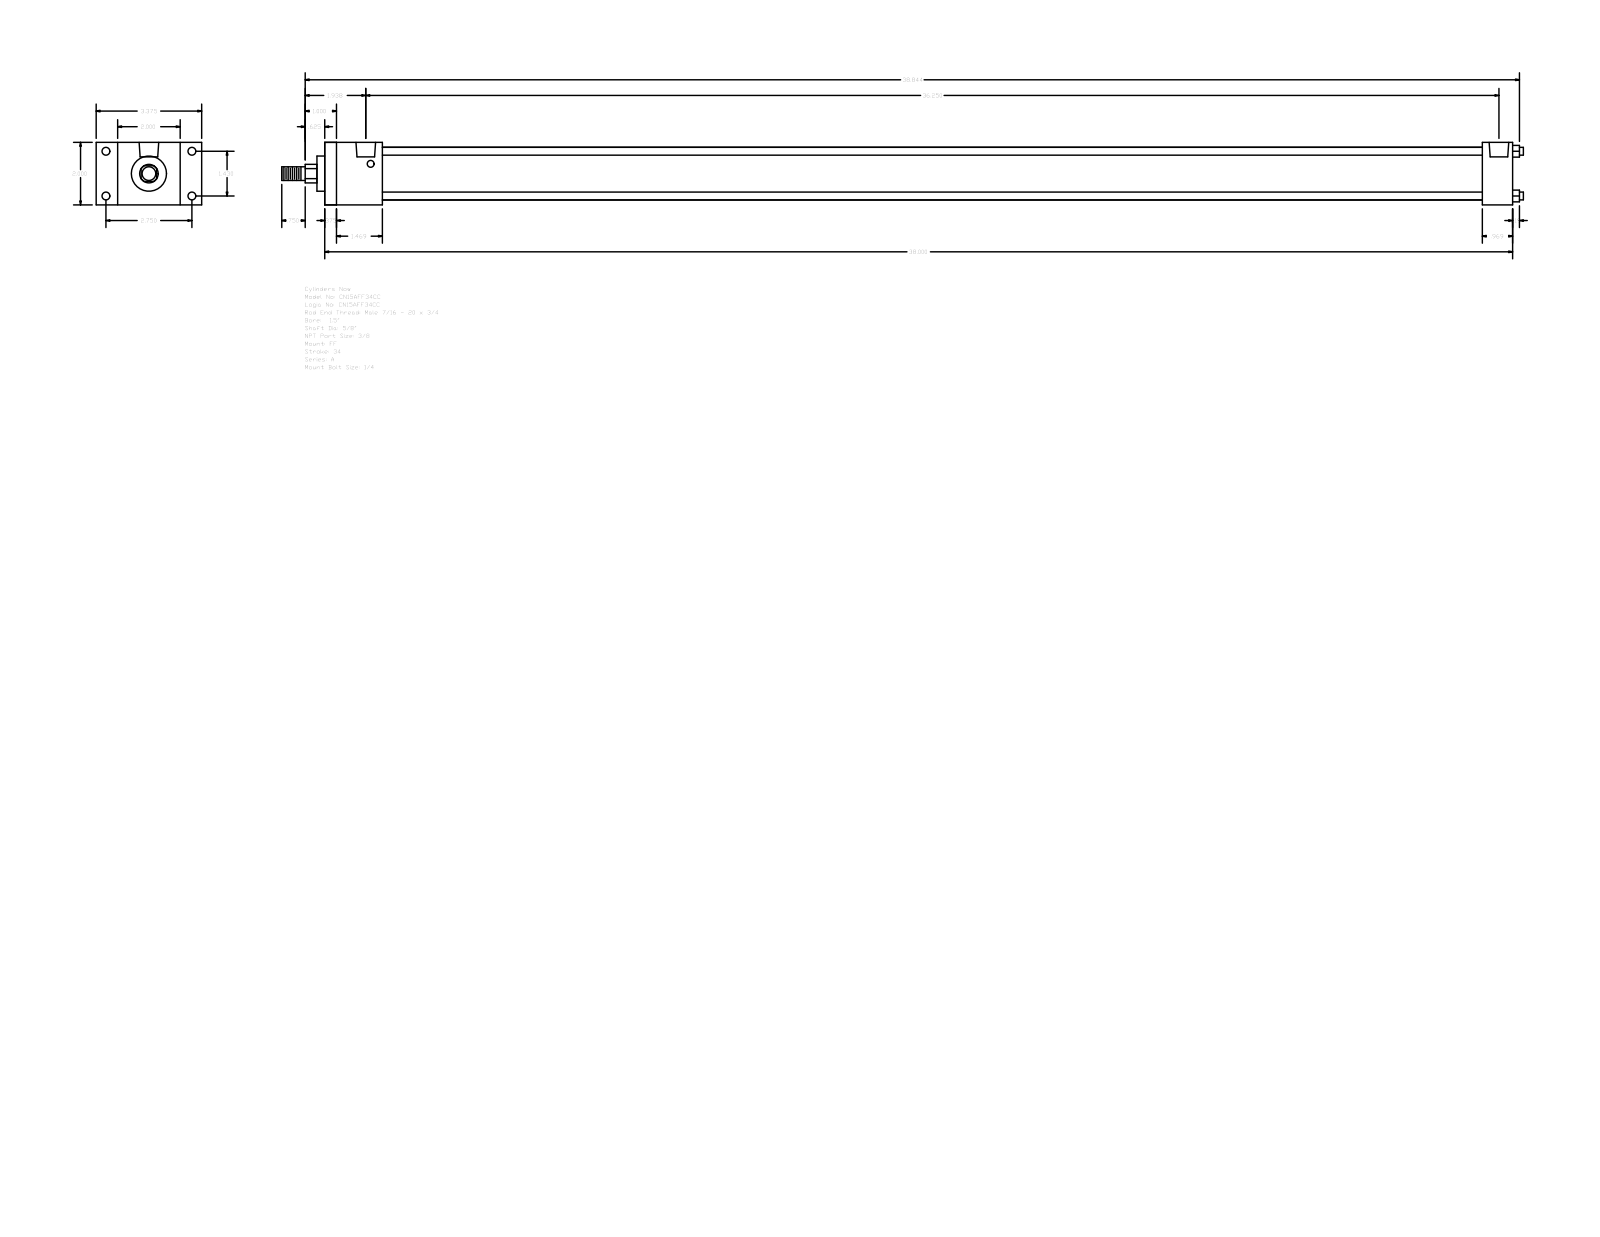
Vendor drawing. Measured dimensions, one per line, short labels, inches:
name: A_FF__0150_0.625
written by: GSSL Pune (CONFIG_CONTROL_DESIGN)
unit: in
bodies: 0 solids, 92 faces (64 planar, 28 cylindrical, 0 other)
size: 39.719 × 3.375 × 2
holes: 4× ⌀0.219, 4× ⌀0.25, 2× ⌀0.627
bosses: 4× ⌀0.25, 1× ⌀1.69, 1× ⌀1.125, 1× ⌀0.625, 1× ⌀0.437
rounds: 1× R0.297
face distances: 2, 38, 0.375, 37.625, 1.844, 37.031, 1.469, 36.656, 35.187, 36.156
hole spacings: 0.156, 1.43, 2.75, 3.099, 35.937, 36.094, 36.25
